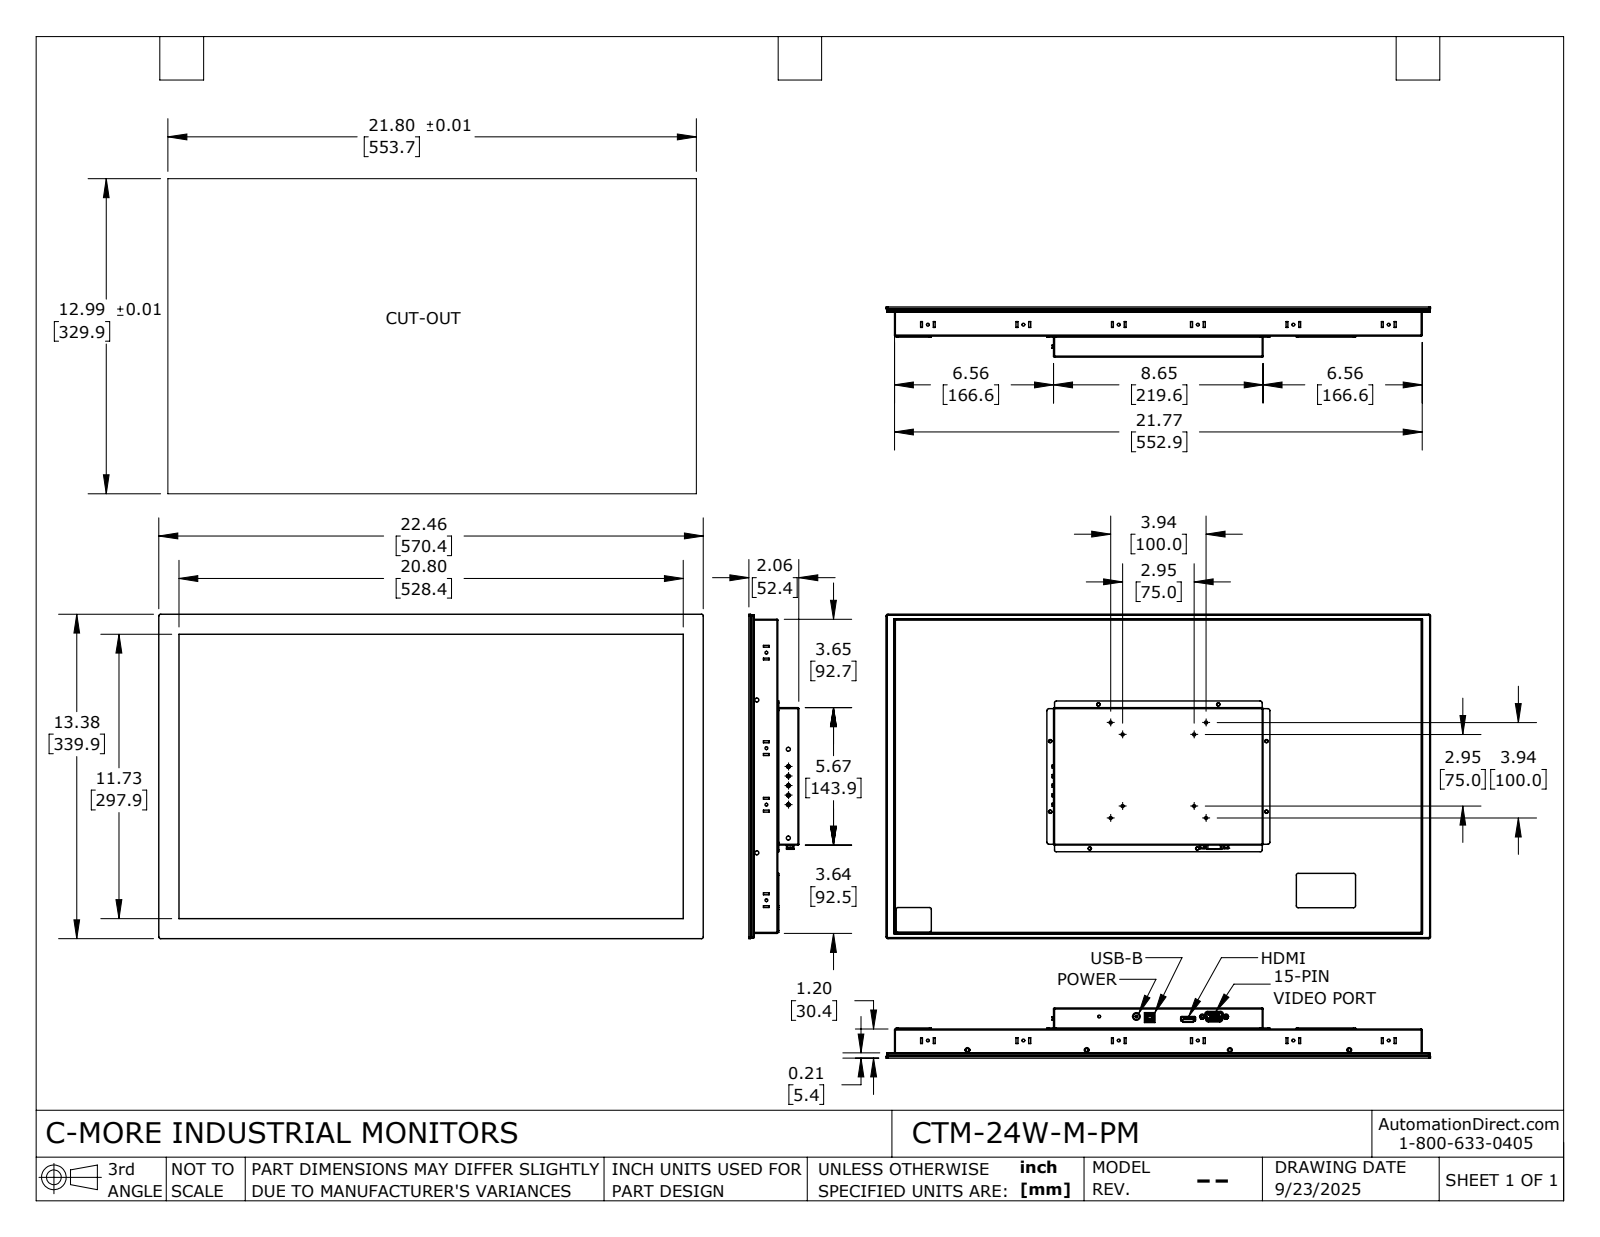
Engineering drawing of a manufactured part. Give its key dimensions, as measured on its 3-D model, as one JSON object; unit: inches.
{"part_name": "CTM-24W-M-PM-20250528", "step_written_by": "SolidWorks 2024 (AUTOMOTIVE_DESIGN)", "units": "inches", "bodies": {"solids": 1, "faces": 1360, "planar": 833, "cylindrical": 443, "other": 84}, "overall_size": [22.458, 13.38, 2.065], "volume_in3": 381.3, "surface_area_in2": 795.5, "round_holes": [[0.118, 19], [0.047, 15], [0.165, 12], [0.125, 8], [0.138, 8], [0.157, 5], [0.108, 2], [0.248, 1], [0.315, 1]], "round_bosses_or_shafts": [[0.128, 2], [0.13, 1], [0.128, 1], [0.127, 1], [0.093, 1]], "partial_cylinders_radius": [[0.006, 60], [0.079, 56], [0.039, 22], [0.118, 8], [0.02, 7], [0.051, 6], [0.063, 6], [0.016, 4]], "face_to_face_distances": [1.191, 1.198, 0.866, 2.057, 2.065, 0.039, 12.954, 1.102, 1.063, 1.994], "hole_center_spacings": [0.09, 0.238, 0.156, 0.09, 3.937, 0.18, 0.18, 3.48]}
